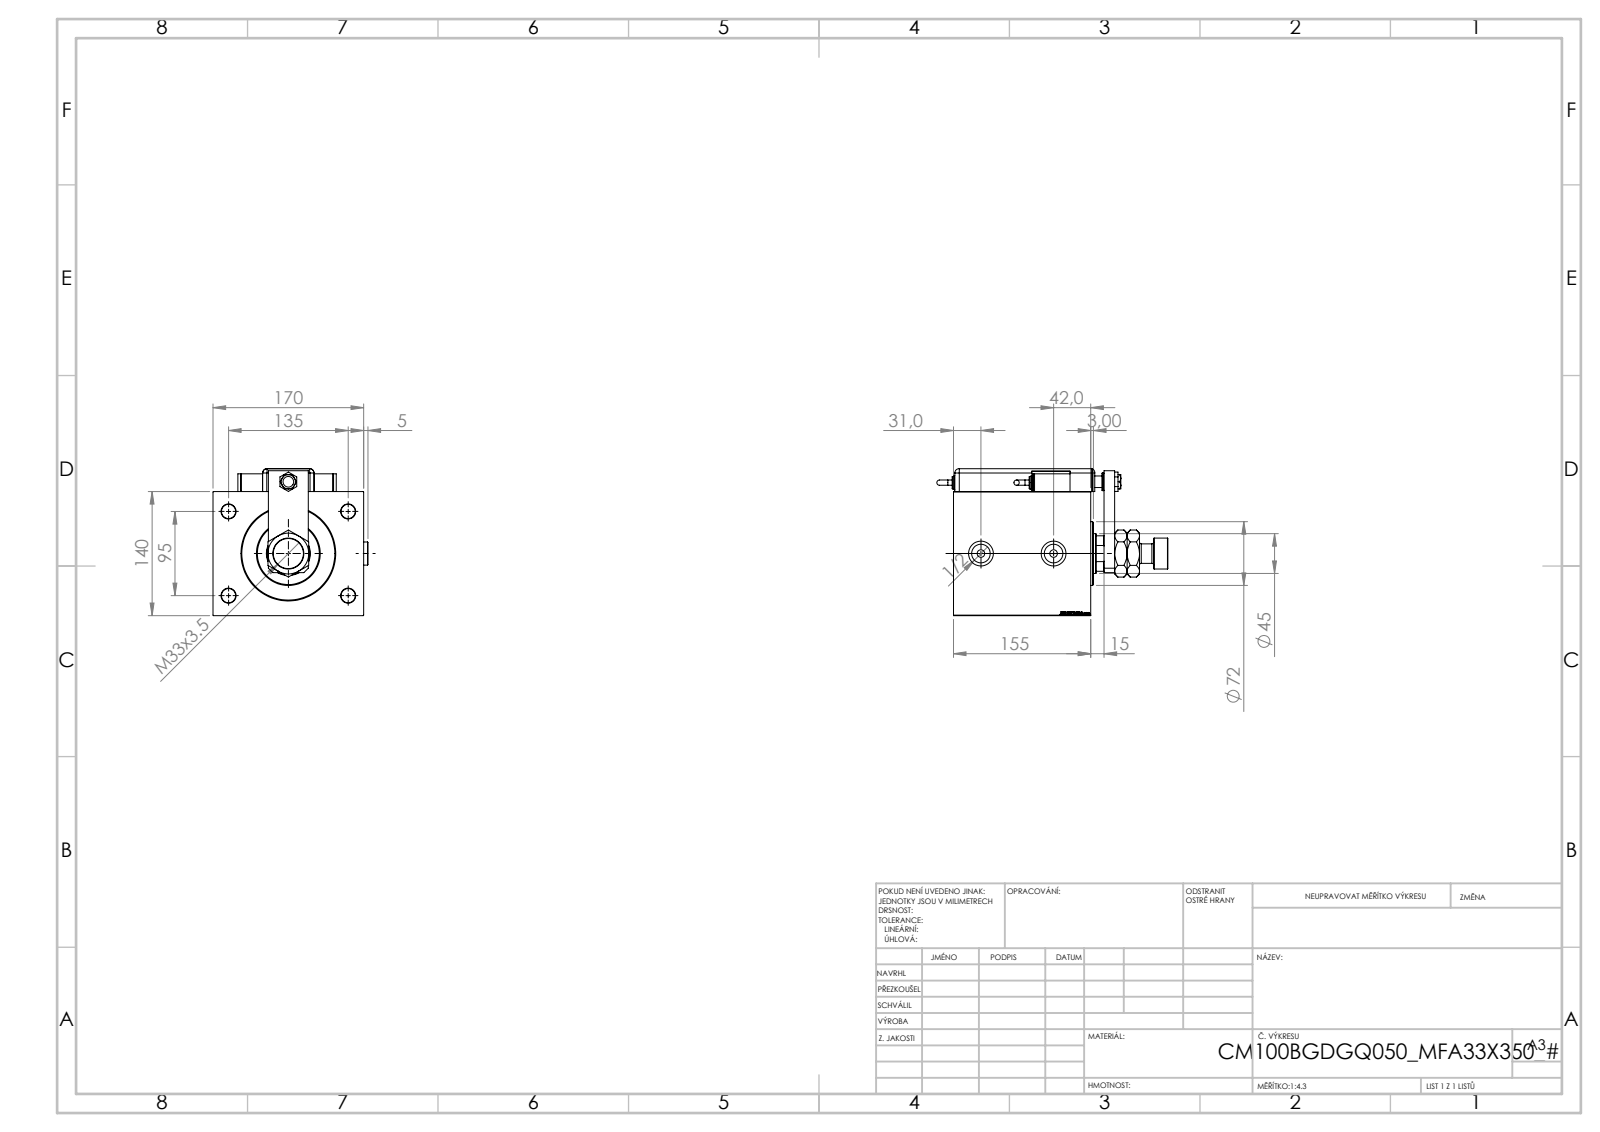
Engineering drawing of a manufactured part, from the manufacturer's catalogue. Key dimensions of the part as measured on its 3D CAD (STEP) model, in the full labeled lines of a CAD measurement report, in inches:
Part name (STEP PRODUCT): TYC; SWITCH_Q_FRONT_BACK; Zatka_OIL_PORT; NUT_D19 (+8 more)
STEP written by: SolidWorks 2019 (CONFIG_CONTROL_DESIGN)
Units: inches
Bodies: 16 solids, 1374 faces (658 planar, 131 cylindrical, 585 other)
Overall size (bounding box): 10.266 × 6.886 × 6.528
Volume: 218.4 in³ · Surface area: 566.5 in²
Round holes (diameter × count): ⌀0.63 ×4, ⌀0.157 ×2, ⌀0.315 ×2, ⌀0.335 ×2, ⌀0.825 ×2, ⌀1.102 ×2, ⌀0.472 ×1, ⌀0.512 ×1, ⌀0.551 ×1, ⌀1.24 ×1, ⌀1.299 ×1, ⌀1.772 ×1
Round bosses / shafts (diameter × count): ⌀0.787 ×3, ⌀1.024 ×2, ⌀0.63 ×2, ⌀0.551 ×2, ⌀0.236 ×2, ⌀2.835 ×1, ⌀1.378 ×1, ⌀0.866 ×1
Partial cylindrical surfaces — rounded edges, fillets, slot ends (radius × count): R0.197 ×9, R0.394 ×1, R0.866 ×1
Main face-to-face distances: 5.512, 6.693, 6.102, 0.118, 1.024, 5.079, 0.591, 4.488, 0.059, 1.016
Hole centre spacings: 3.25, 2.967, 3.74, 5.315, 5.715, 6.499, 0.787, 3.189
